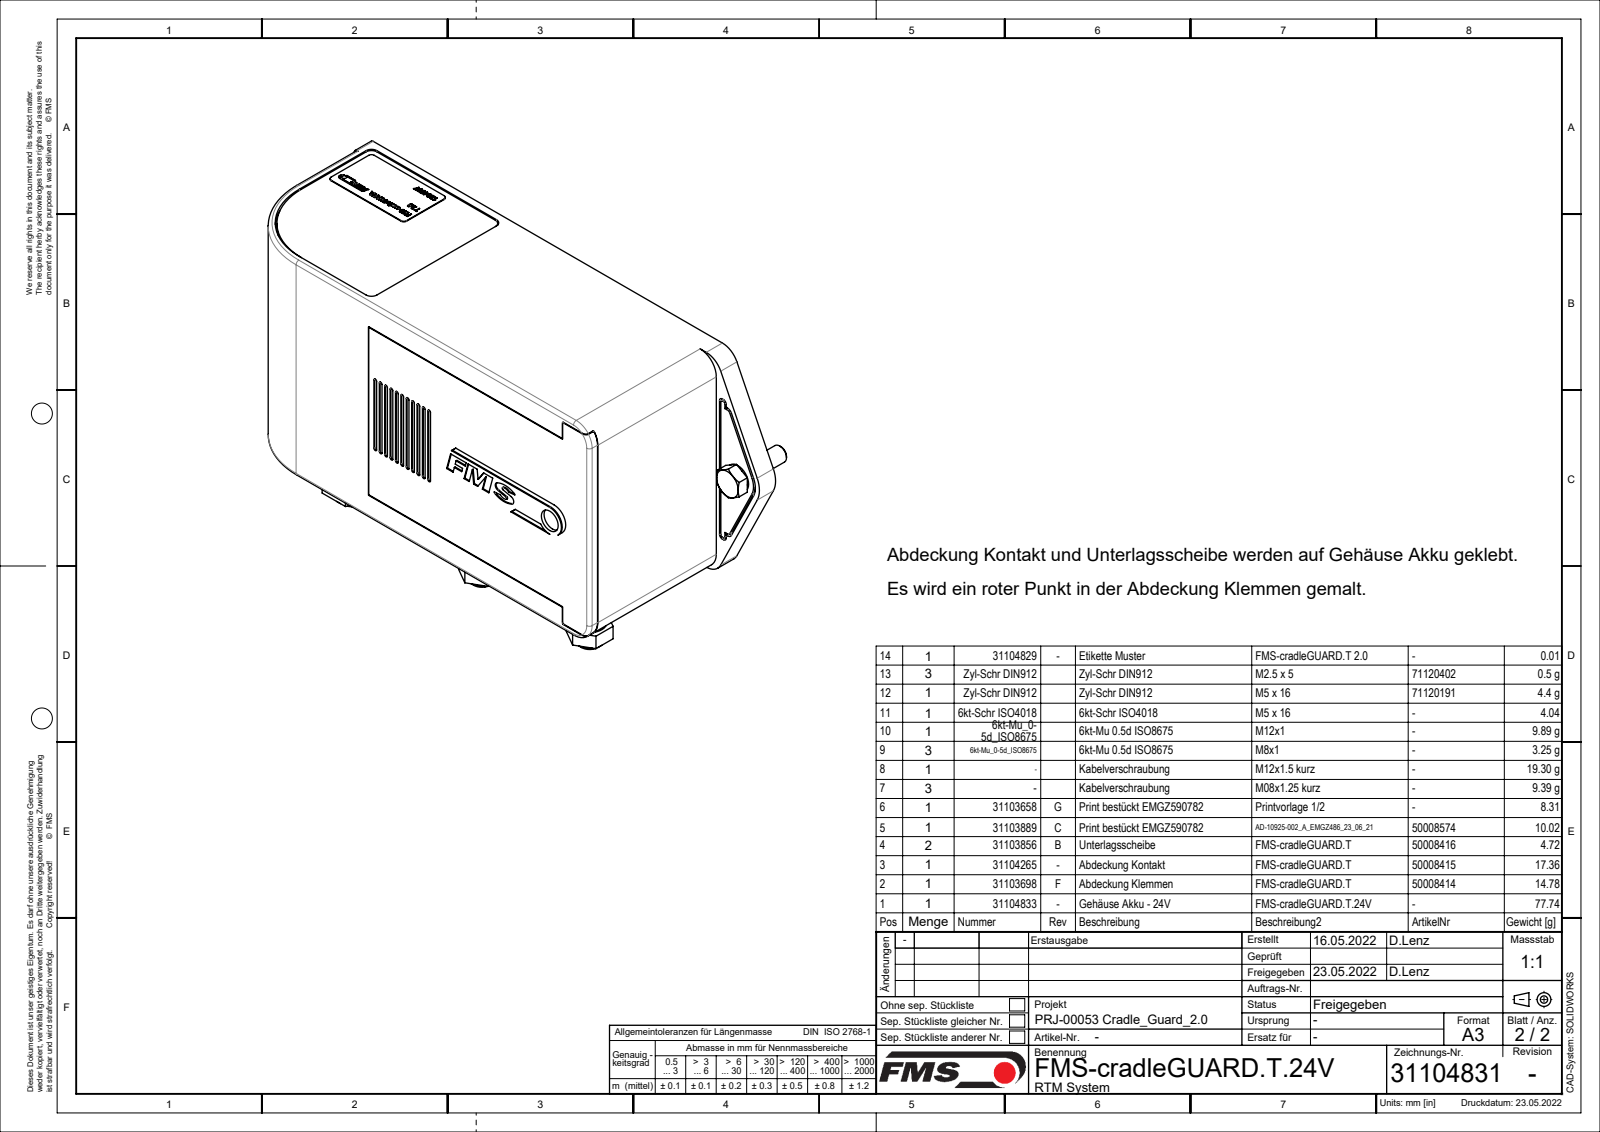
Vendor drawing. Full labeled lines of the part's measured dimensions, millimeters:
Part name (STEP PRODUCT): Zyl-Schr DIN912_M5x16; 6kt-Mu_0-5d_ISO8675_M12x1; 31104831_stp; 6kt-Mu_0-5d_ISO8675_M8x1 (+8 more)
STEP written by: SolidWorks 2018 (CONFIG_CONTROL_DESIGN)
Units: millimetres
Bodies: 16 solids, 1327 faces (610 planar, 332 cylindrical, 385 other)
Overall size (bounding box): 166 × 86 × 63
Volume: 95 374 mm³ · Surface area: 95 756 mm²
Round holes (diameter × count): ⌀1.85 ×3, ⌀2.65 ×3, ⌀4 ×3, ⌀7 ×3, ⌀8.4 ×3, ⌀5.2 ×2, ⌀5.5 ×2, ⌀1.4 ×1, ⌀6.24 ×1, ⌀7.5 ×1, ⌀11 ×1, ⌀12.4 ×1
Round bosses / shafts (diameter × count): ⌀8 ×4, ⌀9 ×3, ⌀4.65 ×3, ⌀5 ×2, ⌀13 ×1, ⌀12 ×1, ⌀8.5 ×1
Partial cylindrical surfaces — rounded edges, fillets, slot ends (radius × count): R0.5 ×80, R1 ×44, R2 ×17, R0.3 ×16, R6 ×10, R0.11 ×2, R0.2 ×2, R0.27 ×2
Main face-to-face distances: 2, 67, 51, 53, 1, 3, 50, 48, 69, 4
Hole centre spacings: 23.85, 56.22, 21.43, 22.88, 23.46, 27.2, 36.81, 40
